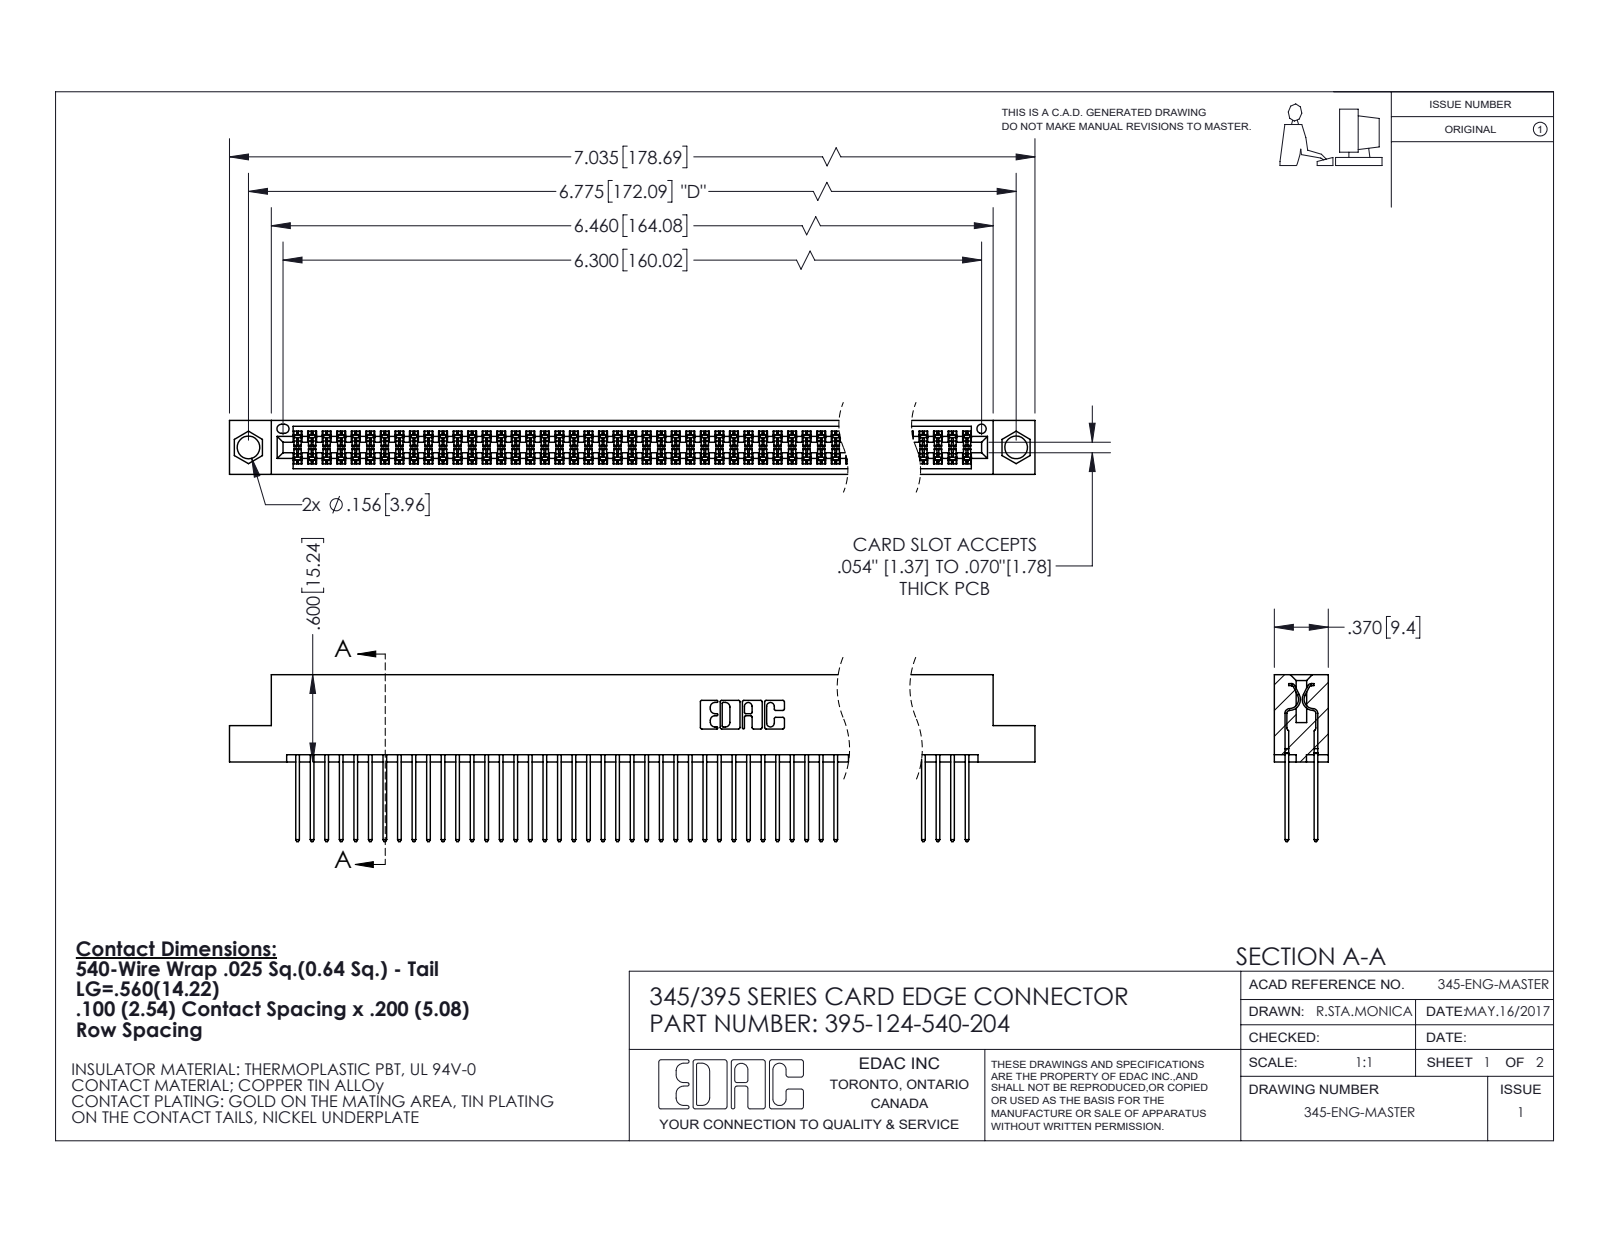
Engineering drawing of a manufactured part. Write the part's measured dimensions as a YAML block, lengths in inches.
part_name: "395-124-540-204; 345 Part_Flush Mounting Lugs - 0.156 Dia-TI; 345-292-001_345-293-140"
step_written_by: "SolidWorks 2020 (CONFIG_CONTROL_DESIGN)"
units: inches
bodies: {solids: 125, faces: 6340, planar: 4186, cylindrical: 2154, other: 0}
overall_size: [7.035, 1.147, 0.37]
volume: 1.093
surface_area: 44.78
round_holes:
  - {diameter: 0.156, count: 2}
  - {diameter: 0.064, count: 1}
partial_cylinders:
  - {radius: 0.006, count: 186}
  - {radius: 0.01, count: 124}
  - {radius: 0.01, count: 22}
  - {radius: 0.007, count: 6}
  - {radius: 0.031, count: 6}
  - {radius: 0.026, count: 3}
  - {radius: 0.014, count: 2}
  - {radius: 0.019, count: 2}
face_to_face_distances: [0.298, 0.072, 0.2, 0.098, 0.272, 0.025, 0.37, 0.225, 0.175, 0.149]
hole_center_spacings: [0.27, 6.539, 6.775]
